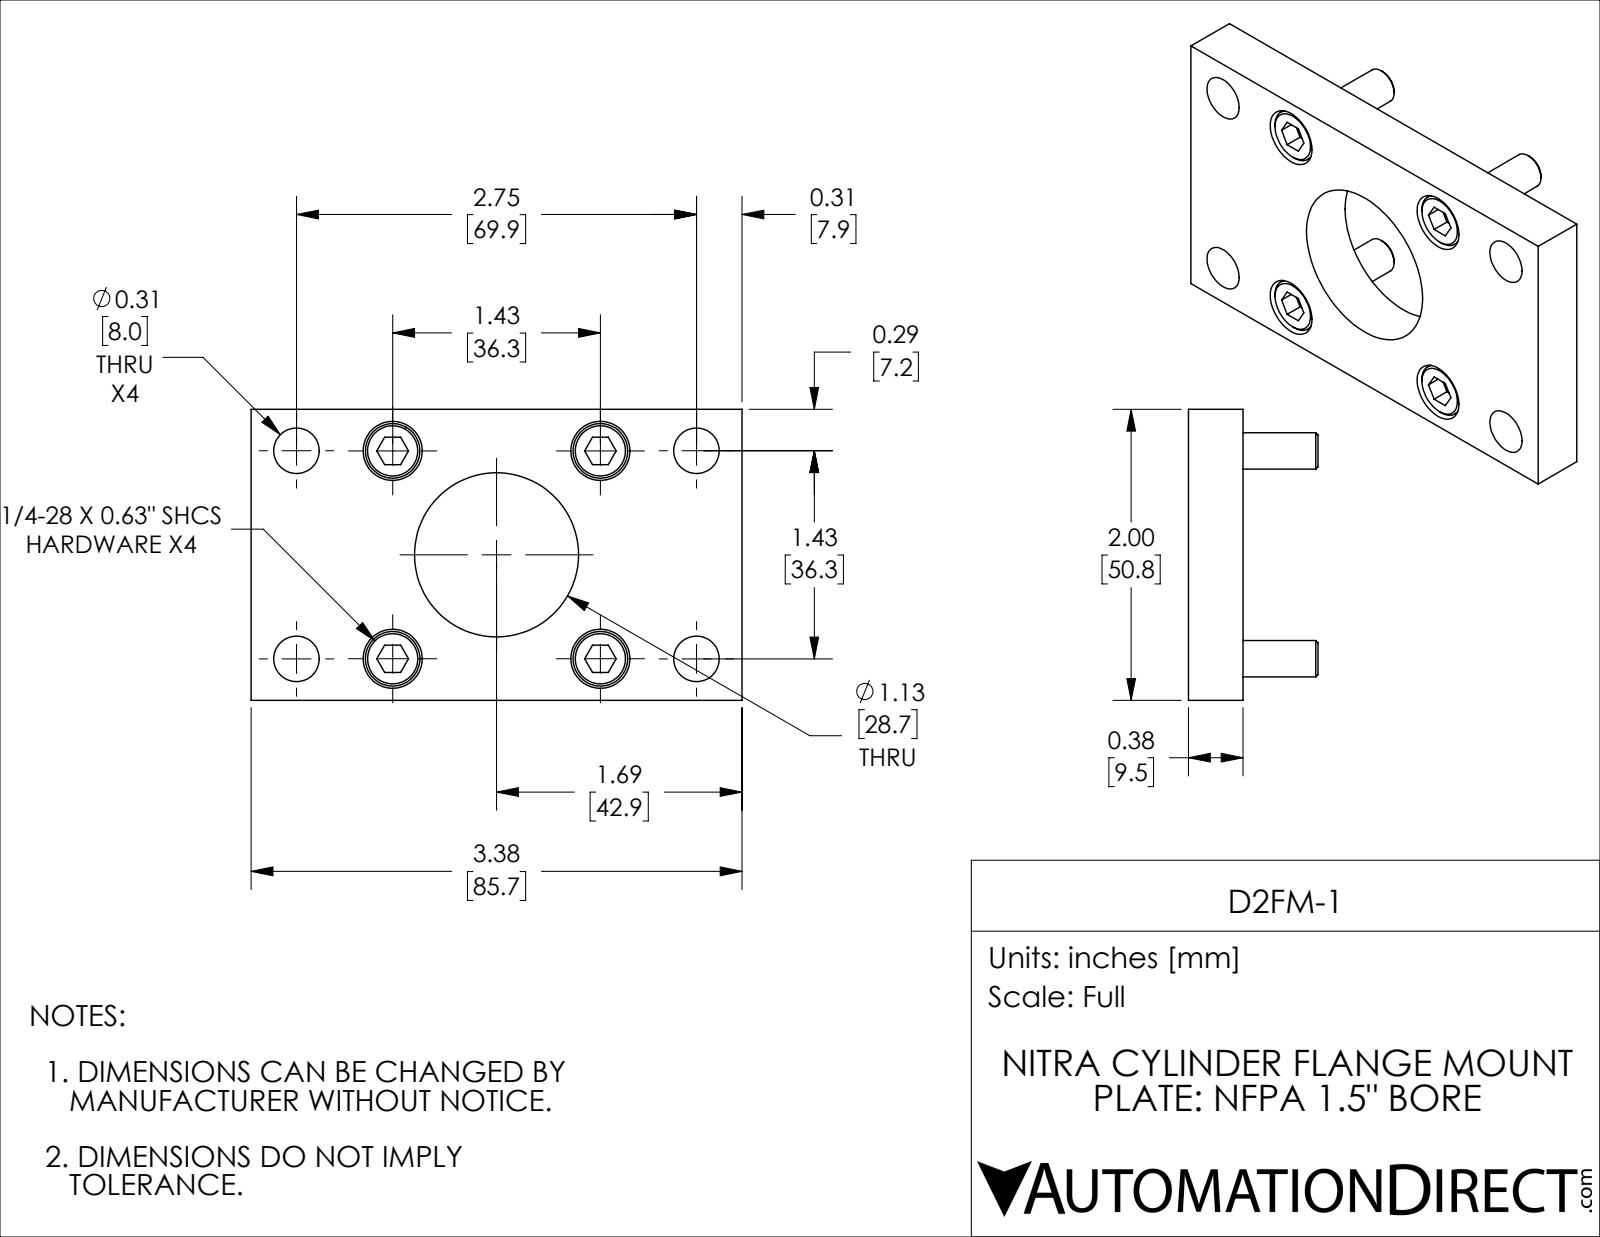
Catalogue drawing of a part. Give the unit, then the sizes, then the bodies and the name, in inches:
Units: inches
Overall size (bounding box): 3.375 × 2 × 0.891
Round holes (diameter × count): ⌀0.281 ×4, ⌀0.313 ×4, ⌀0.406 ×4, ⌀1.128 ×1
Round bosses / shafts (diameter × count): ⌀0.25 ×4, ⌀0.375 ×2, ⌀0.375 ×2
Main face-to-face distances: 0.375, 2, 3.375, 0.109, 0.266, 0.359, 0.25, 0.016, 0.516, 0.625
Hole centre spacings: 1.01, 1.428, 1.574, 0.661, 0.661, 1.43, 1.55, 1.55
Volume: 2.093 in³ · Surface area: 23.25 in²
Bodies: 5 solids, 108 faces (50 planar, 42 cylindrical, 16 other)
Part name (STEP PRODUCT): D2FM-1
STEP written by: SolidWorks 2019 (CONFIG_CONTROL_DESIGN)
